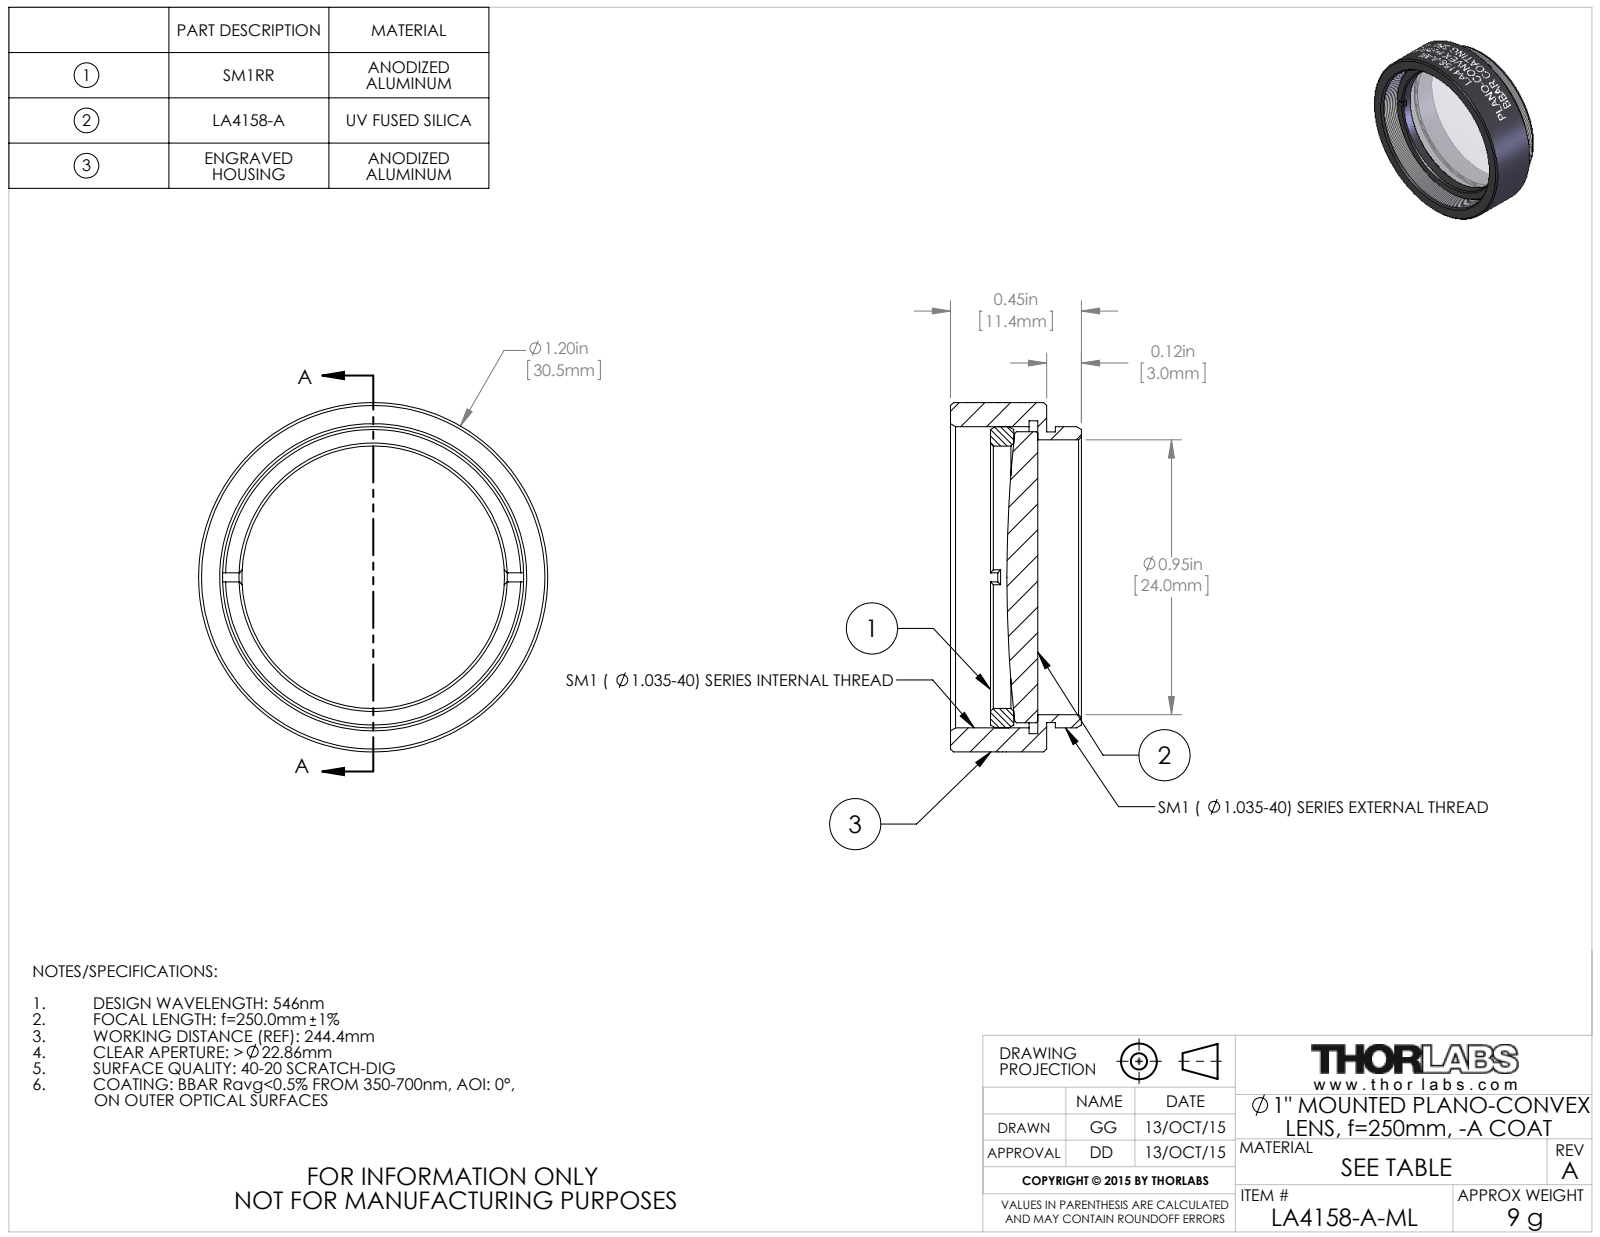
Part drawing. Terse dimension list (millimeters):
name: TTN039180-E0W
written by: SolidWorks 2014 (CONFIG_CONTROL_DESIGN)
unit: mm
bodies: 3 solids, 160 faces (20 planar, 112 cylindrical, 28 other)
size: 30.48 × 30.48 × 11.43
volume: 3 271 mm³; area: 4 302 mm²
holes: 1× ⌀22.91, 1× ⌀24, 1× ⌀26.29, 1× ⌀27.31
bosses: 1× ⌀30.48, 1× ⌀26.29, 1× ⌀25.4, 1× ⌀25.37
face distances: 0.76, 8.38, 7.62, 2.87, 2.11, 5.51, 4.9, 4.14, 2.03, 3.48
